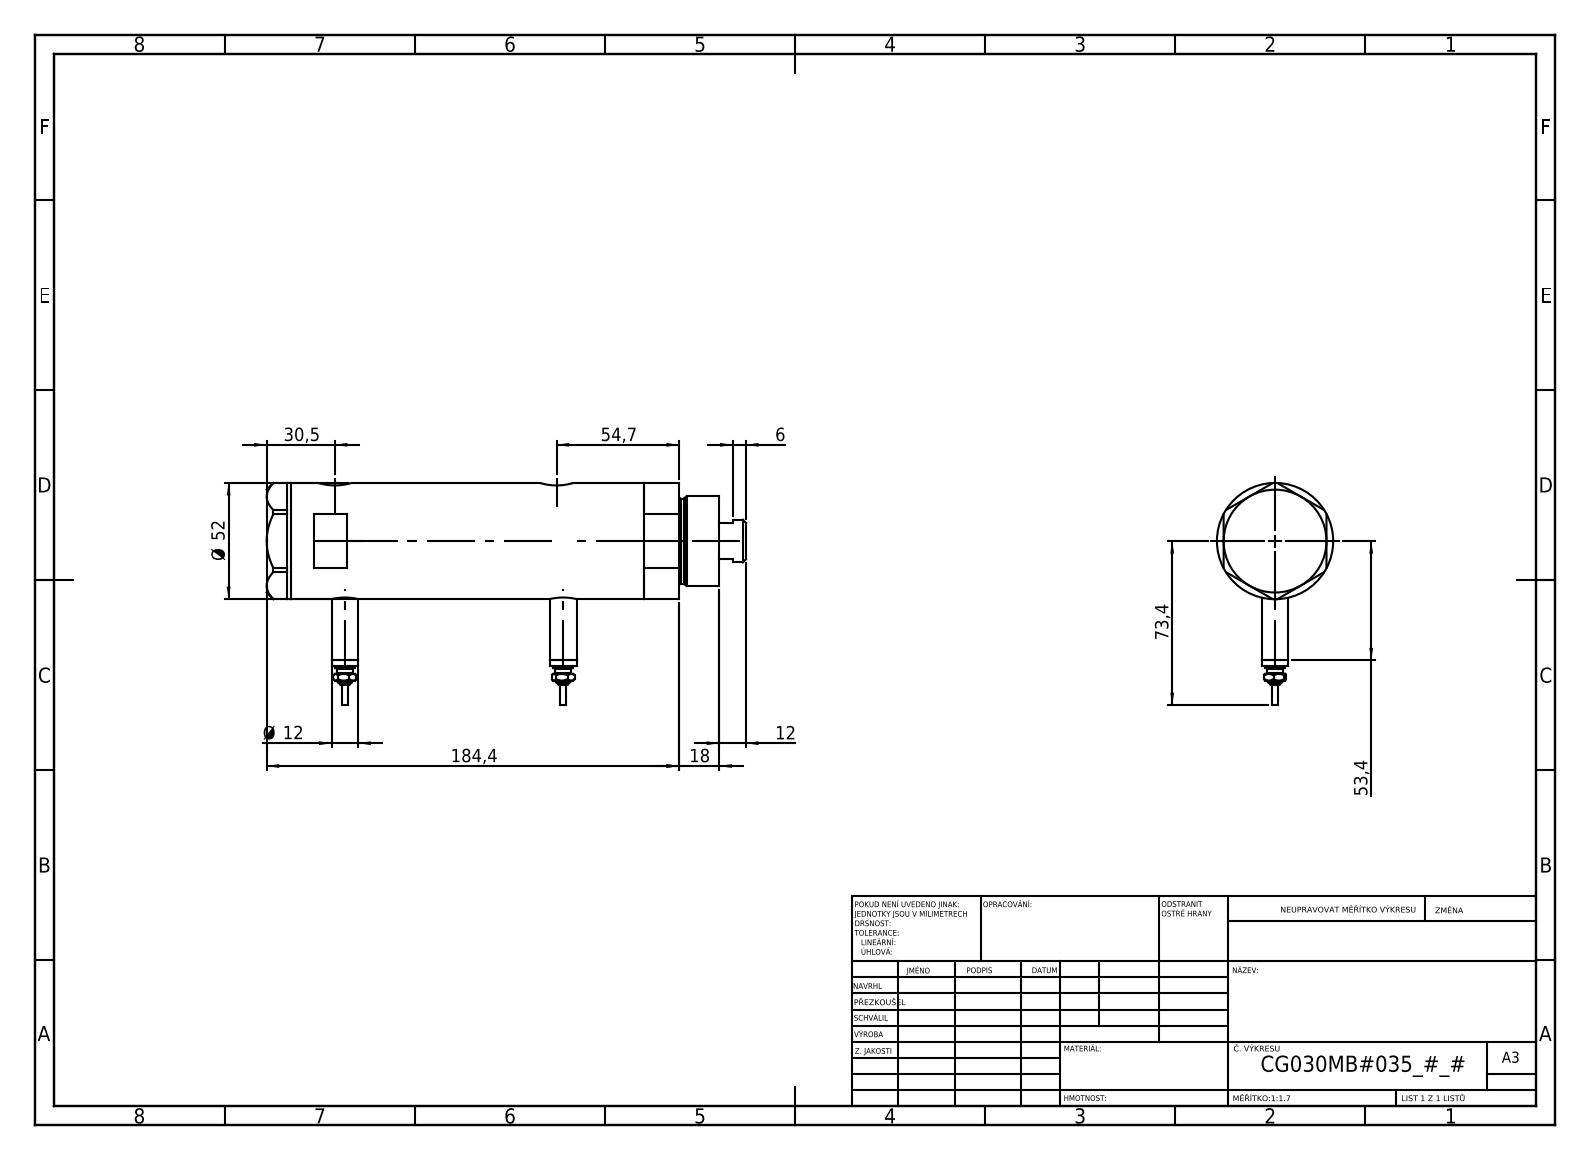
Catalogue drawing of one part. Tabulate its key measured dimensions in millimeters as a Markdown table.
| quantity | value |
| --- | --- |
| part name | V270CG_FRONT; Switch; V270CG_BACK; V270CG_VC (+1 more) |
| STEP written by | SolidWorks 2019 (CONFIG_CONTROL_DESIGN) |
| units | millimeters |
| bodies | 6 solids, 226 faces (93 planar, 69 cylindrical, 64 other) |
| overall size | 214.4 × 99.4 × 52 |
| volume | 402 682 mm³ |
| surface area | 90 312 mm² |
| round holes (diameter × count) | 9.73 × 2, 12.5 × 2, 15 × 2, 6.5 × 1, 20 × 1, 21.5 × 1, 30 × 1, 33 × 1, 44 × 1 |
| round bosses / shafts (diameter × count) | 12 × 2, 9 × 2, 7 × 2, 4.5 × 2, 2.5 × 2, 52 × 1, 40 × 1, 38 × 1 |
| main face-to-face distances | 121.5, 23.8, 97.7, 11, 34.8, 132.5, 46, 36.4, 168.9, 157.9 |
| hole center spacings | 2.9, 4.5, 94.7, 97.6, 99.2, 102.1 |
